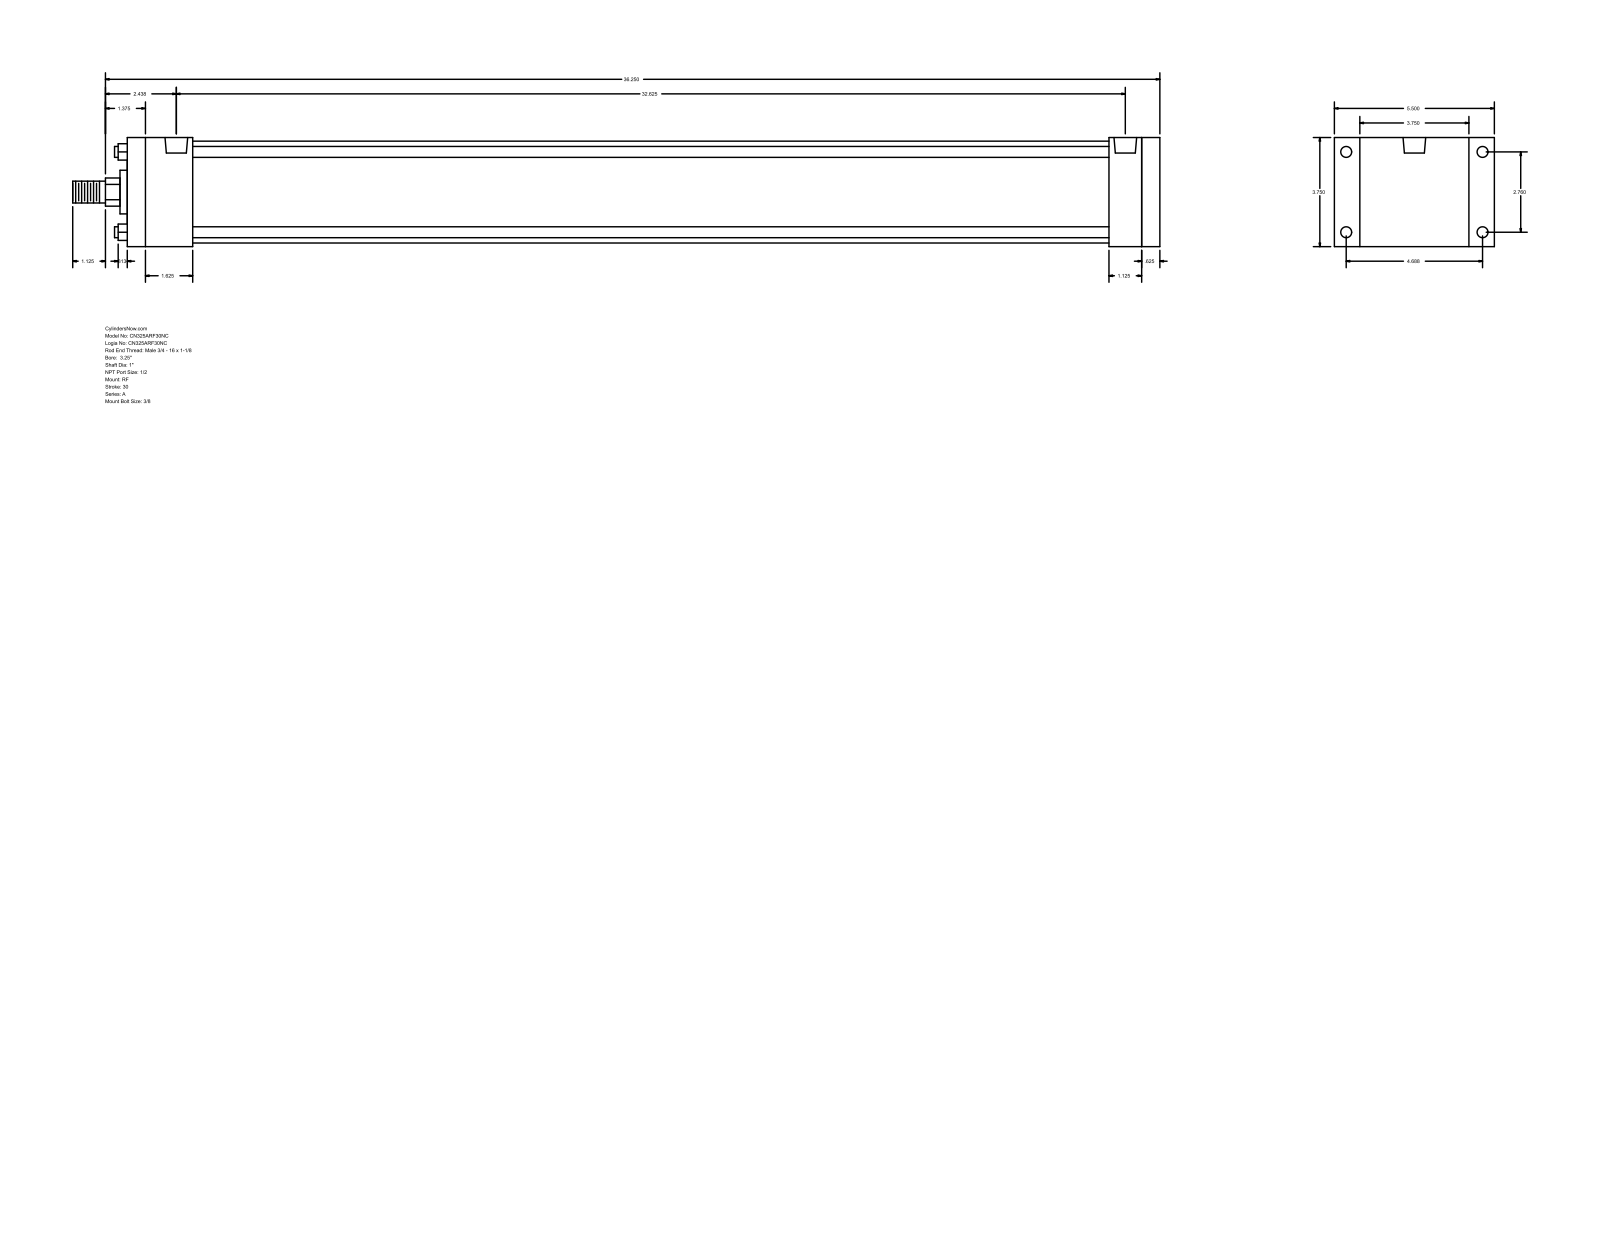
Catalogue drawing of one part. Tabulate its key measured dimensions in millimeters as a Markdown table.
| quantity | value |
| --- | --- |
| part name | A_RF__0325_1 |
| STEP written by | GSSL Pune (CONFIG_CONTROL_DESIGN) |
| units | millimeters |
| bodies | 0 solids, 92 faces (64 planar, 28 cylindrical, 0 other) |
| overall size | 949.33 × 139.7 × 95.25 |
| round holes (diameter × count) | 8.73 × 4, 9.53 × 4, 19.77 × 2 |
| round bosses / shafts (diameter × count) | 9.53 × 4, 88.9 × 1, 38.1 × 1, 25.4 × 1, 19.05 × 1 |
| partial cylindrical surfaces (radius × count) | 12.29 × 1 |
| main face-to-face distances | 95.24, 901.7, 885.83, 15.87, 22.23, 117.47, 857.25, 28.58, 44.45, 57.15 |
| hole center spacings | 3.18, 70.1, 119.06, 138.16, 822.32, 825.5, 828.68 |
